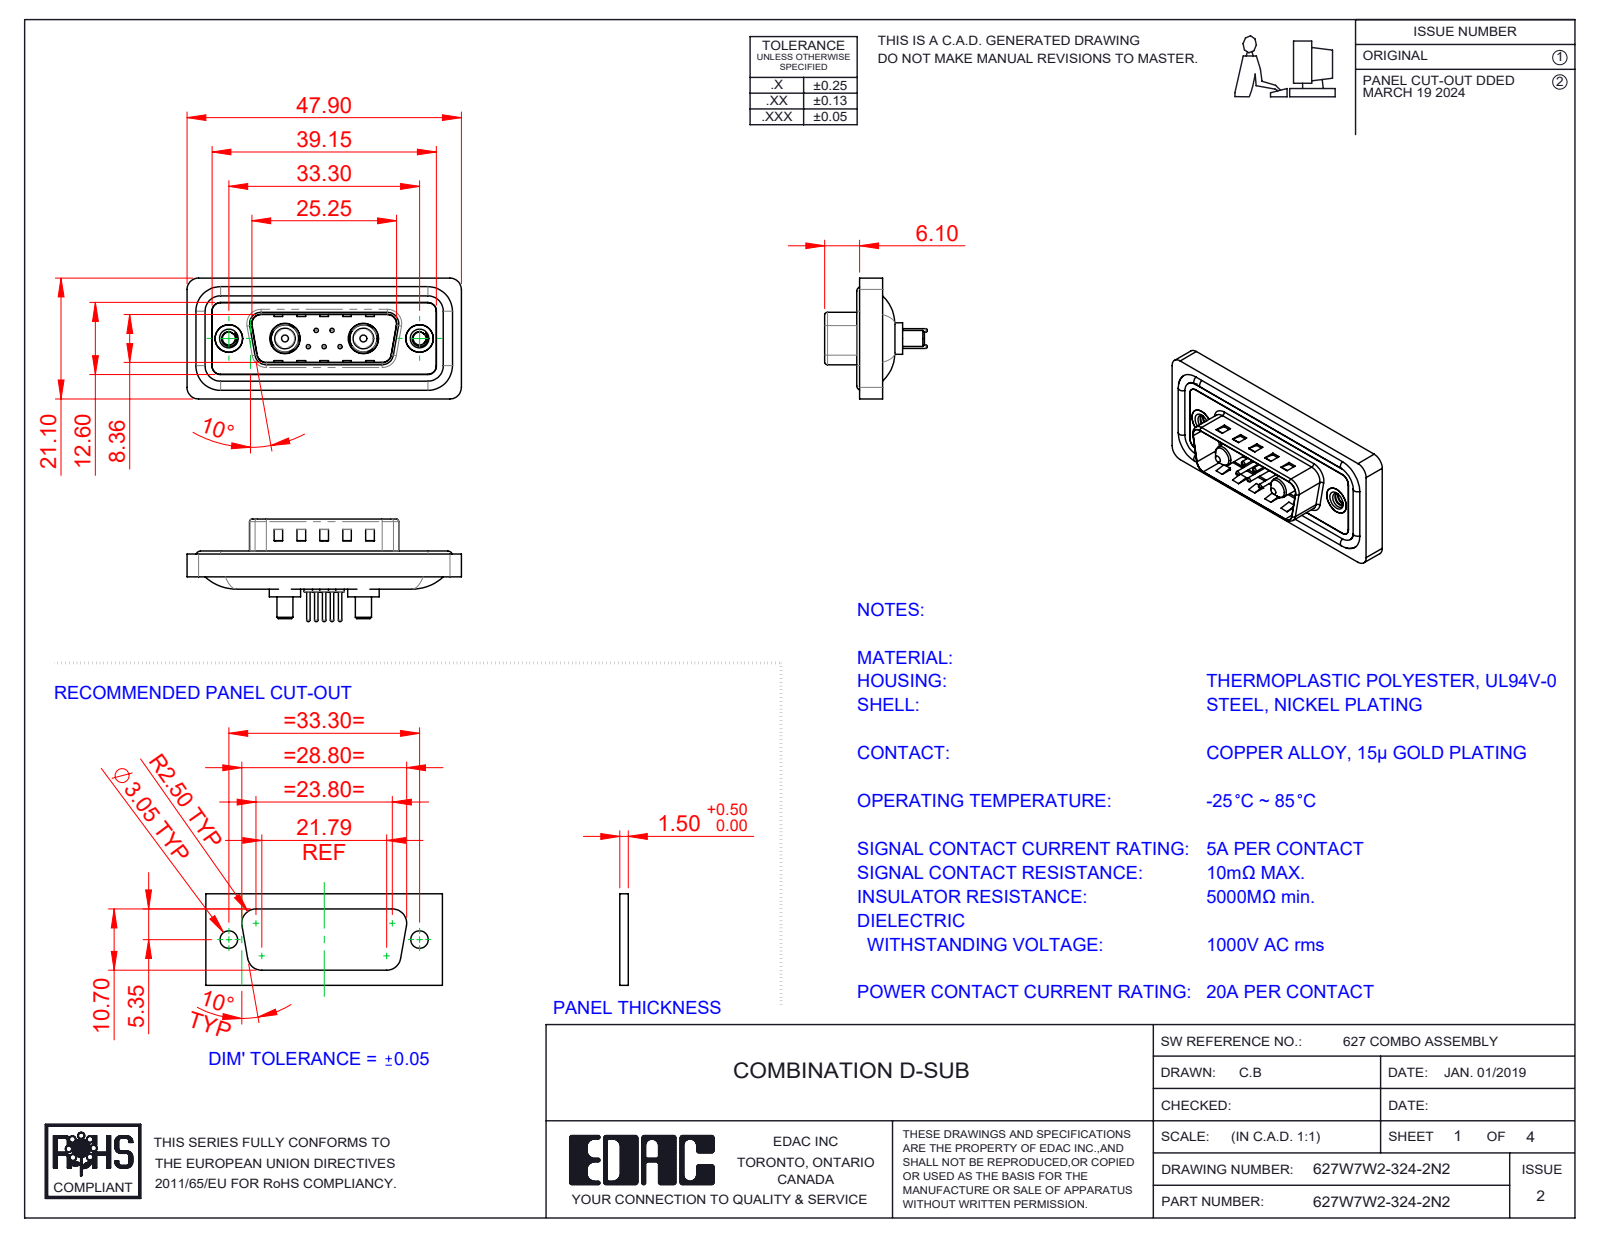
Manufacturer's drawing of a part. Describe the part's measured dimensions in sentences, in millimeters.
The part is named "627Combo Threaded Rivet_2; 627Combo Shell Rear_15 Contacts; 627Combo Shell Front_15 Contacts; Power Pin_20A S (+5 more)". Its 3-D file was written by "SolidWorks 2023 (CONFIG_CONTROL_DESIGN)". It is 16 solids with 710 faces: 232 planar, 292 cylindrical and 186 other. Overall it measures 47.9 by 21.1 by 17.9 millimeters. Its volume is 5 517 cubic millimeters and its surface area 8 793 square millimeters. Round holes: 5 of diameter 0.75, 5 of diameter 1.6, 5 of diameter 2, 2 of diameter 2.26, 2 of diameter 4, 2 of diameter 4.8, 2 of diameter 4.85, 2 of diameter 5, 2 of diameter 5.3. Round bosses or shafts: 5 of diameter 1.5, 5 of diameter 0.6, 4 of diameter 1.6, 2 of diameter 5.5, 2 of diameter 5.2, 2 of diameter 4.9, 2 of diameter 4.75, 2 of diameter 3.75. Partial cylindrical surfaces (rounded edges, fillets, slot ends): 26 of radius 1.5, 20 of radius 2, 8 of radius 0.5, 8 of radius 1.6, 4 of radius 0.25, 4 of radius 0.6, 4 of radius 0.65, 4 of radius 0.9. The main face-to-face distances are 0.4, 1.1, 1.5, 1.6, 0.5, 3.1, 2.9, 0.82, 9.58, 4. The hole center spacings are 3.16, 2.77, 9.8, 23.5, 4.31, 4.33, 5.03, 5.04.
